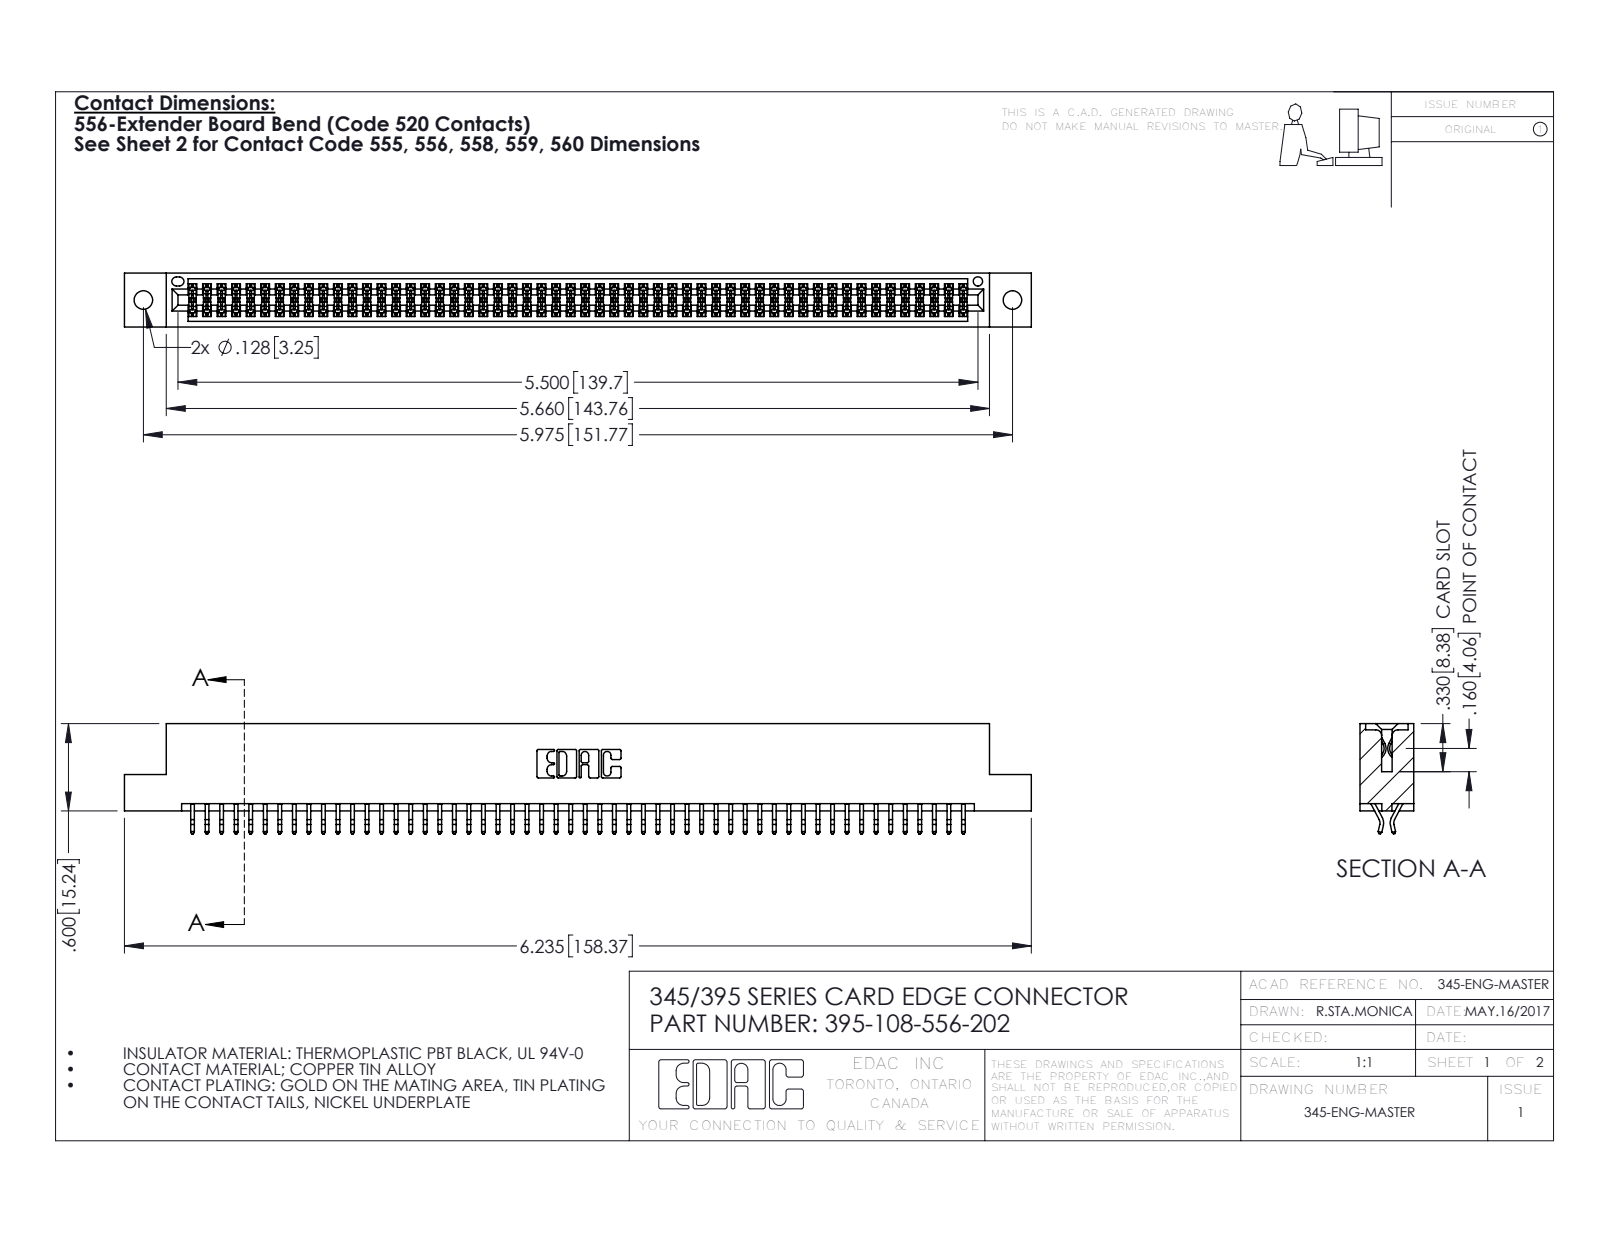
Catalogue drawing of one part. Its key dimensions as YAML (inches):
part_name: "345-292-001_556 Tail; 395-108-556-202; 345 Part_Flush Mounting Lugs - 0.128 Dia"
step_written_by: "SolidWorks 2016 (CONFIG_CONTROL_DESIGN)"
units: inches
bodies: {solids: 109, faces: 6174, planar: 4076, cylindrical: 2098, other: 0}
overall_size: [6.235, 0.757, 0.37]
volume: 0.943
surface_area: 35.2
round_holes:
  - {diameter: 0.128, count: 2}
  - {diameter: 0.064, count: 1}
partial_cylinders:
  - {radius: 0.006, count: 162}
  - {radius: 0.01, count: 22}
  - {radius: 0.007, count: 6}
  - {radius: 0.031, count: 6}
  - {radius: 0.026, count: 3}
  - {radius: 0.01, count: 2}
  - {radius: 0.014, count: 2}
  - {radius: 0.019, count: 2}
face_to_face_distances: [0.298, 0.072, 0.37, 0.2, 0.025, 0.098, 0.272, 0.225, 0.175, 0.149]
hole_center_spacings: [0.27, 5.739, 5.975]
